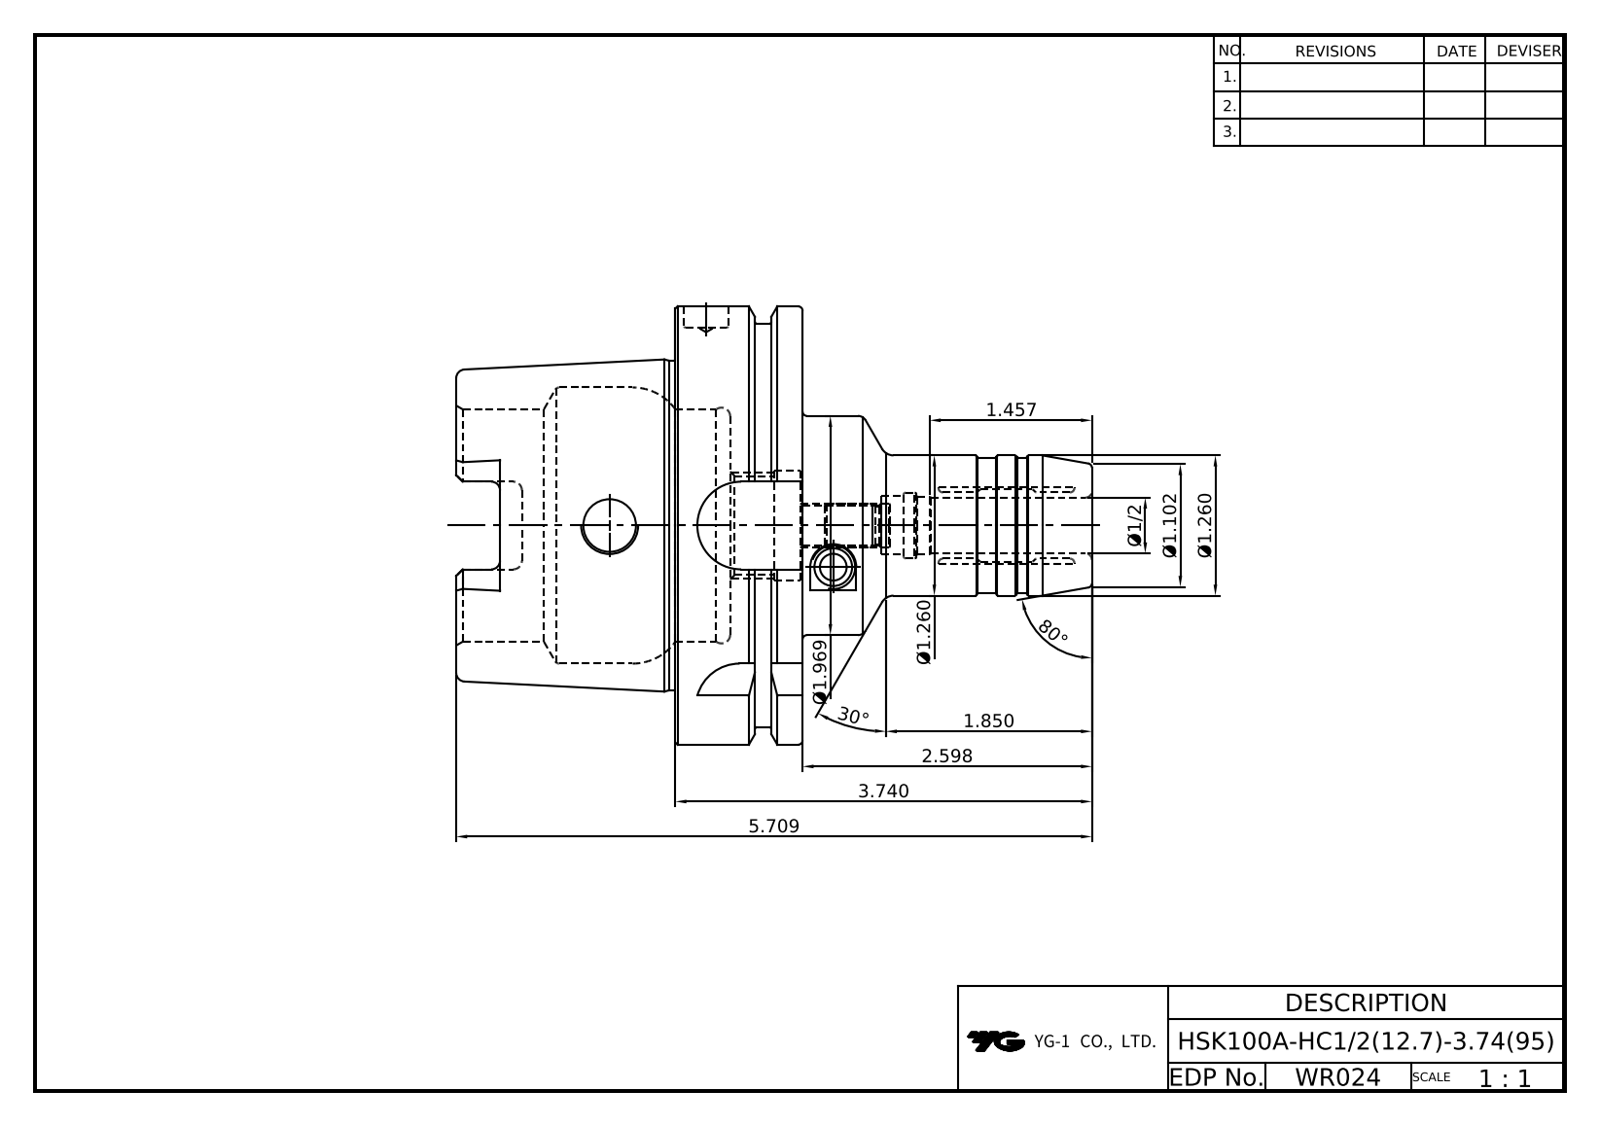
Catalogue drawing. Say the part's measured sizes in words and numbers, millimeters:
The part is named "HSK100A-HC12.7-95". Its 3-D file was written by "Autodesk Inventor 2020 (AUTOMOTIVE_DESIGN)". It is 1 solid with 136 faces: 39 planar, 40 cylindrical and 57 other. Overall it measures 145 by 100 by 100 millimeters. Its volume is 317 366 cubic millimeters and its surface area 58 731 square millimeters. Round holes: 2 of diameter 12, 1 of diameter 8.92, 1 of diameter 10, 1 of diameter 12.7, 1 of diameter 13.2, 1 of diameter 22.38, 1 of diameter 25, 1 of diameter 53, 1 of diameter 63. Round bosses or shafts: 1 of diameter 100, 1 of diameter 92, 1 of diameter 75.41, 1 of diameter 50, 1 of diameter 32, 1 of diameter 31. Partial cylindrical surfaces (rounded edges, fillets, slot ends): 6 of radius 2, 4 of radius 4.88, 4 of radius 10. The main face-to-face distances are 29, 12.5, 16.5, 62.5, 50, 79, 88, 145, 95, 82.5.
